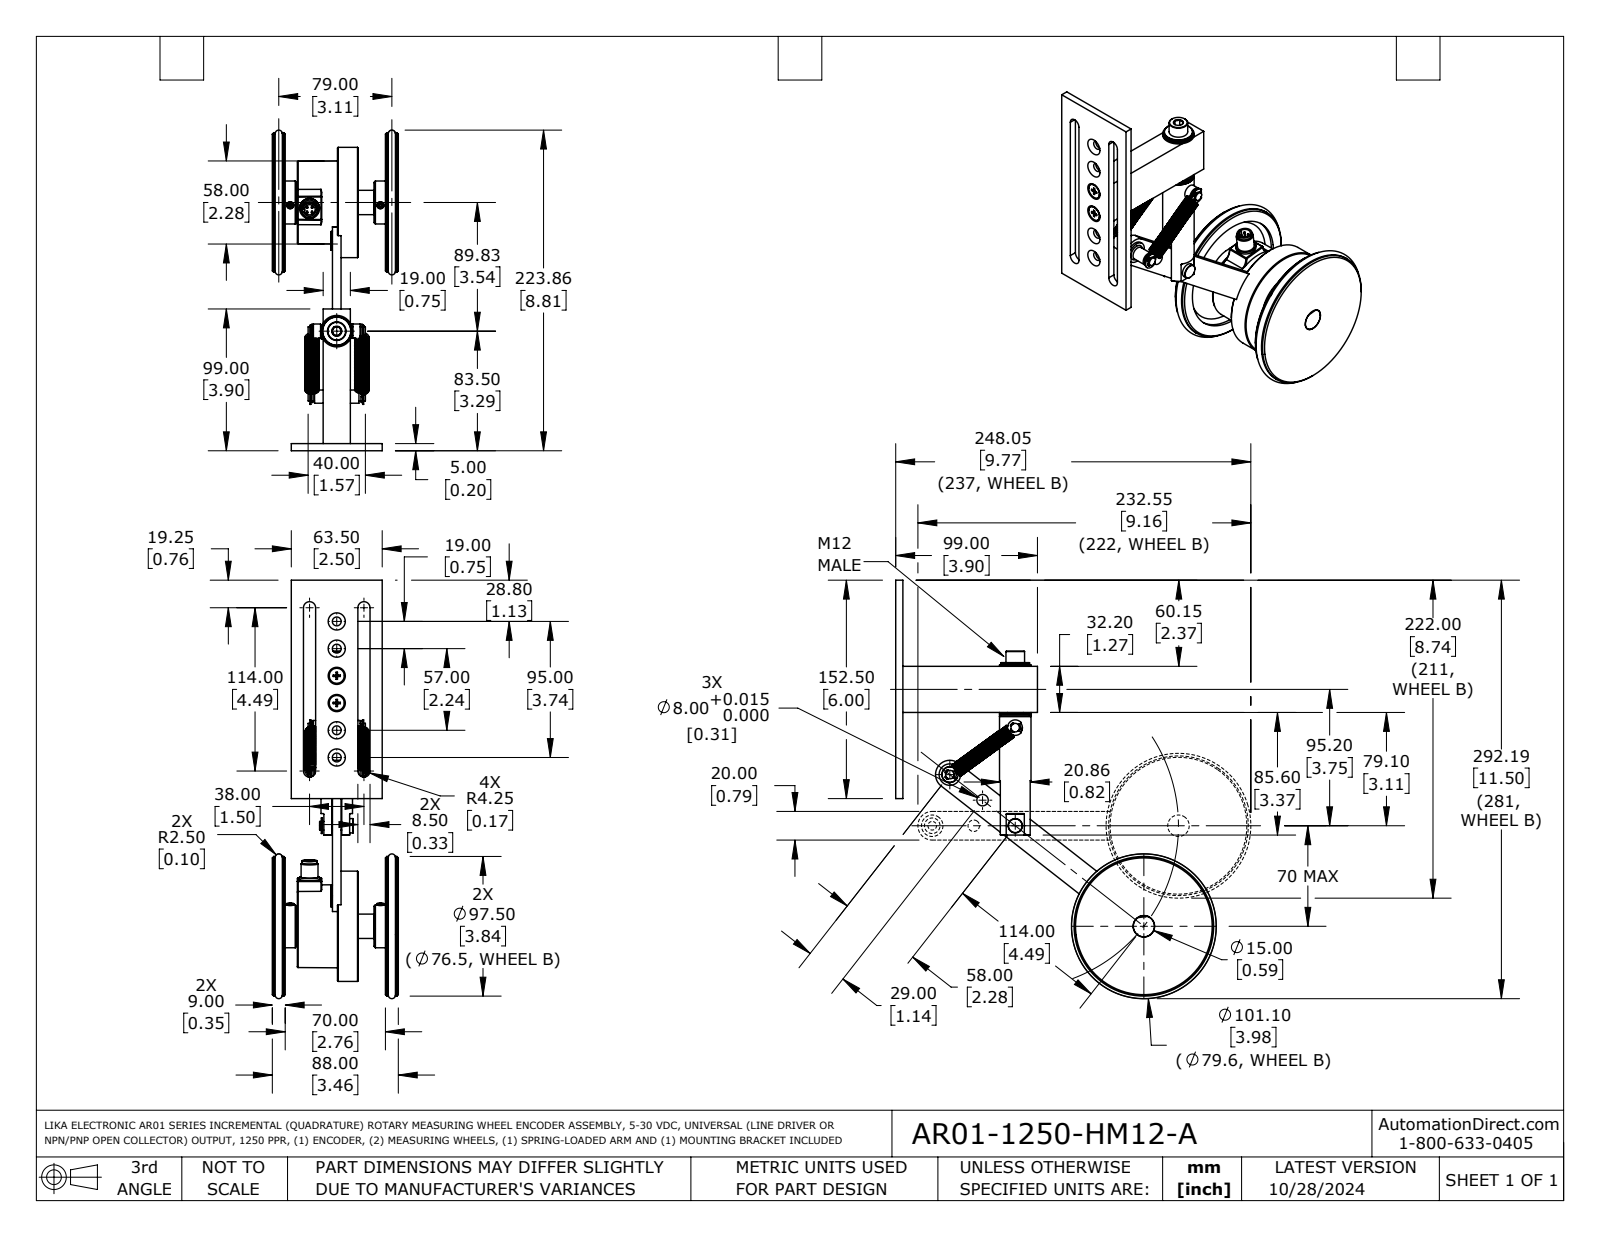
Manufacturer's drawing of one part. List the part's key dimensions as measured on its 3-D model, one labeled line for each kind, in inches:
Part name (STEP PRODUCT): AR01-1250-HM12-A MAIN; AR01-1250-HM12-A TOP PIN HDW; AR01-1250-HM12-A PLATE SCREW; AR01-1250-HM12-A C PIVOT (+6 more)
STEP written by: SolidWorks 2021 (AUTOMOTIVE_DESIGN)
Units: inches
Bodies: 45 solids, 2094 faces (1049 planar, 553 cylindrical, 492 other)
Overall size (bounding box): 11.49 × 8.827 × 3.465
Volume: 20.7 in³ · Surface area: 258.4 in²
Round holes (diameter × count): ⌀0.244 ×8, ⌀0.098 ×6, ⌀0.165 ×4, ⌀0.315 ×3, ⌀0.13 ×2, ⌀0.197 ×2, ⌀0.295 ×2, ⌀0.24 ×1, ⌀0.268 ×1, ⌀0.327 ×1, ⌀0.331 ×1, ⌀0.394 ×1
Round bosses / shafts (diameter × count): ⌀0.236 ×5, ⌀0.197 ×5, ⌀0.055 ×4, ⌀0.049 ×4, ⌀0.031 ×4, ⌀0.118 ×3, ⌀0.787 ×2, ⌀0.63 ×2
Partial cylindrical surfaces — rounded edges, fillets, slot ends (radius × count): R0.02 ×47, R0.008 ×17, R0.007 ×15, R0.167 ×4, R0.03 ×3, R0.081 ×3, R0.148 ×3, R0.214 ×3
Main face-to-face distances: 0.197, 0.256, 0.965, 0.157, 3.465, 1.673, 1.319, 0.354, 3.307, 1.791
Hole centre spacings: 0.748, 0.984, 1.496, 2.244, 0.342, 0.531, 1.142, 1.353
